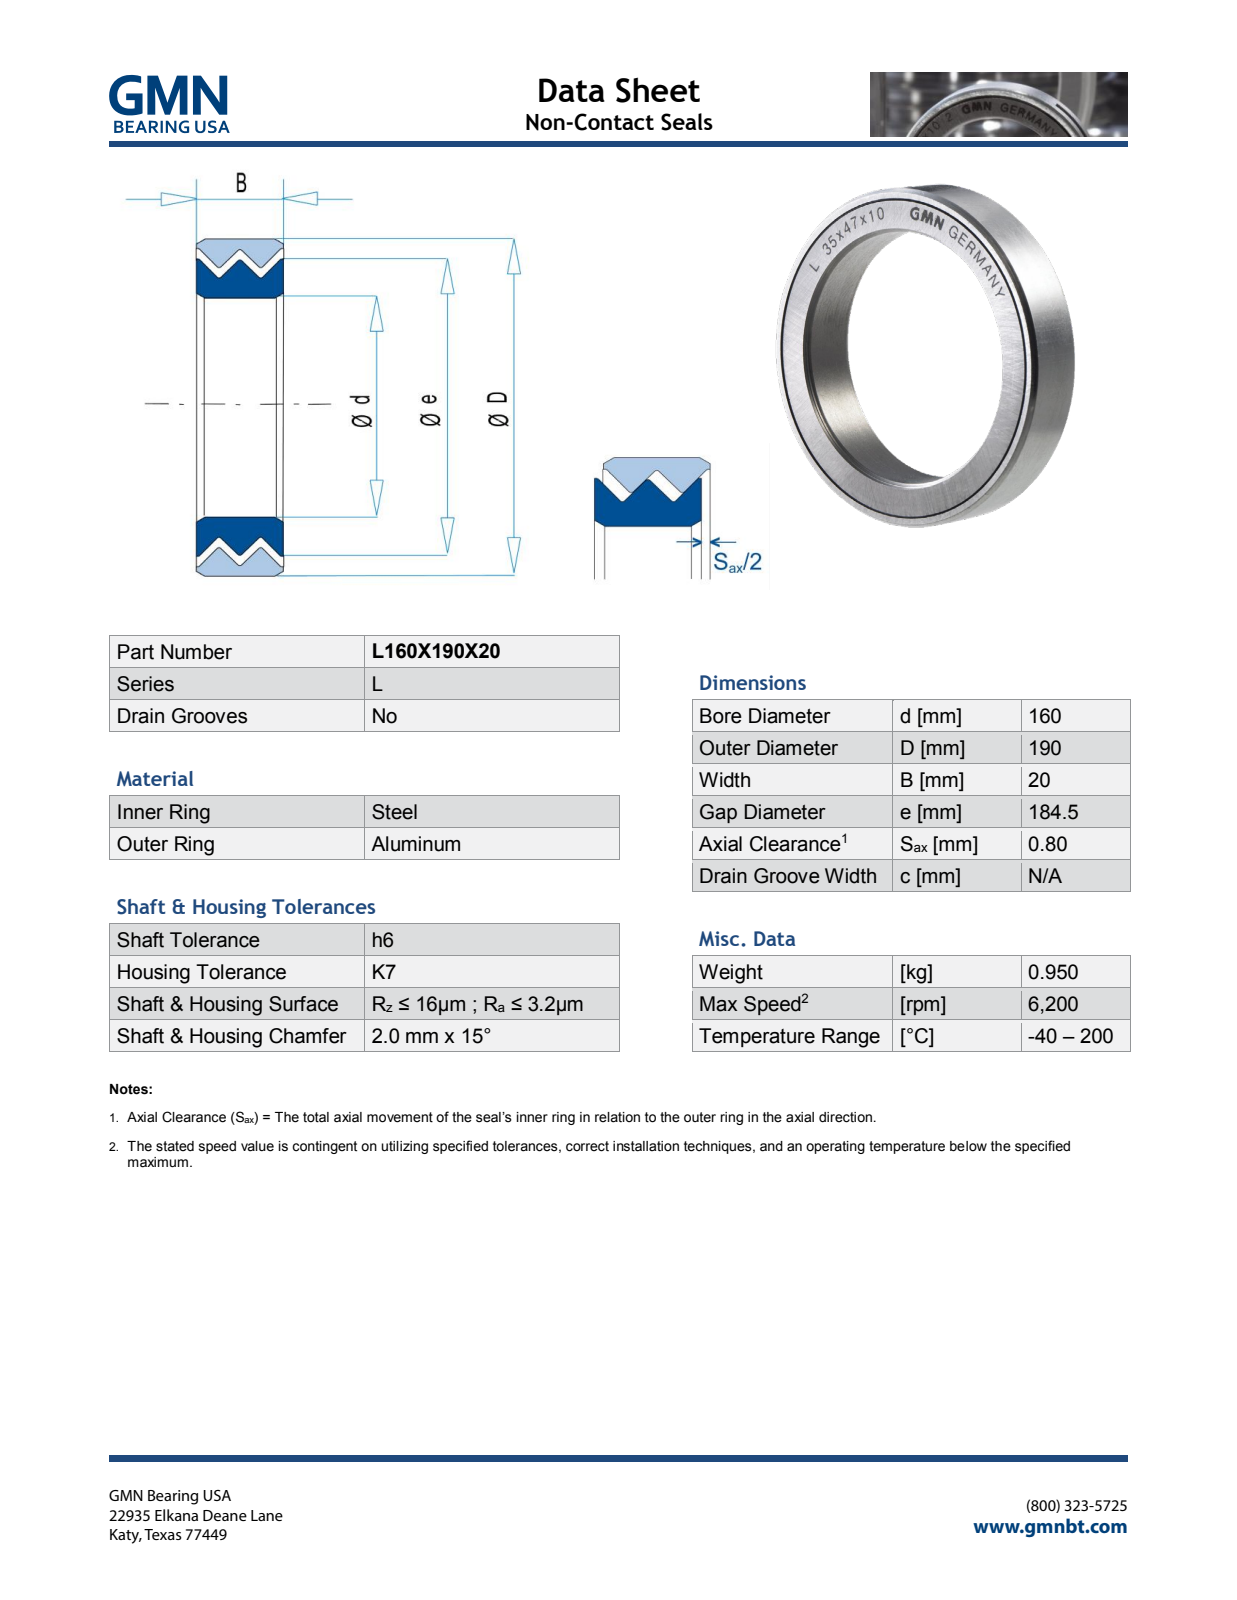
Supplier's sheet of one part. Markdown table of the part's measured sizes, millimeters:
| quantity | value |
| --- | --- |
| part name | L160X190X20_PRT |
| STEP written by | PRO/ENGINEER BY PARAMETRIC TECHNOLOGY CORPORATION, 2013150 (AUTOMOTIVE_DESIGN) |
| units | millimeters |
| bodies | 2 solids, 706 faces (618 planar, 12 cylindrical, 76 other) |
| overall size | 190 × 190 × 20.08 |
| volume | 157 560 mm³ |
| surface area | 68 187 mm² |
| round holes (diameter × count) | 160 × 1, 185.09 × 1 |
| round bosses / shafts (diameter × count) | 190 × 1, 184.5 × 1 |
| main face-to-face distances | 20, 20.08, 1.14, 9.1, 1.13, 1.16, 7.96, 6.82, 1.02, 6.44 |
